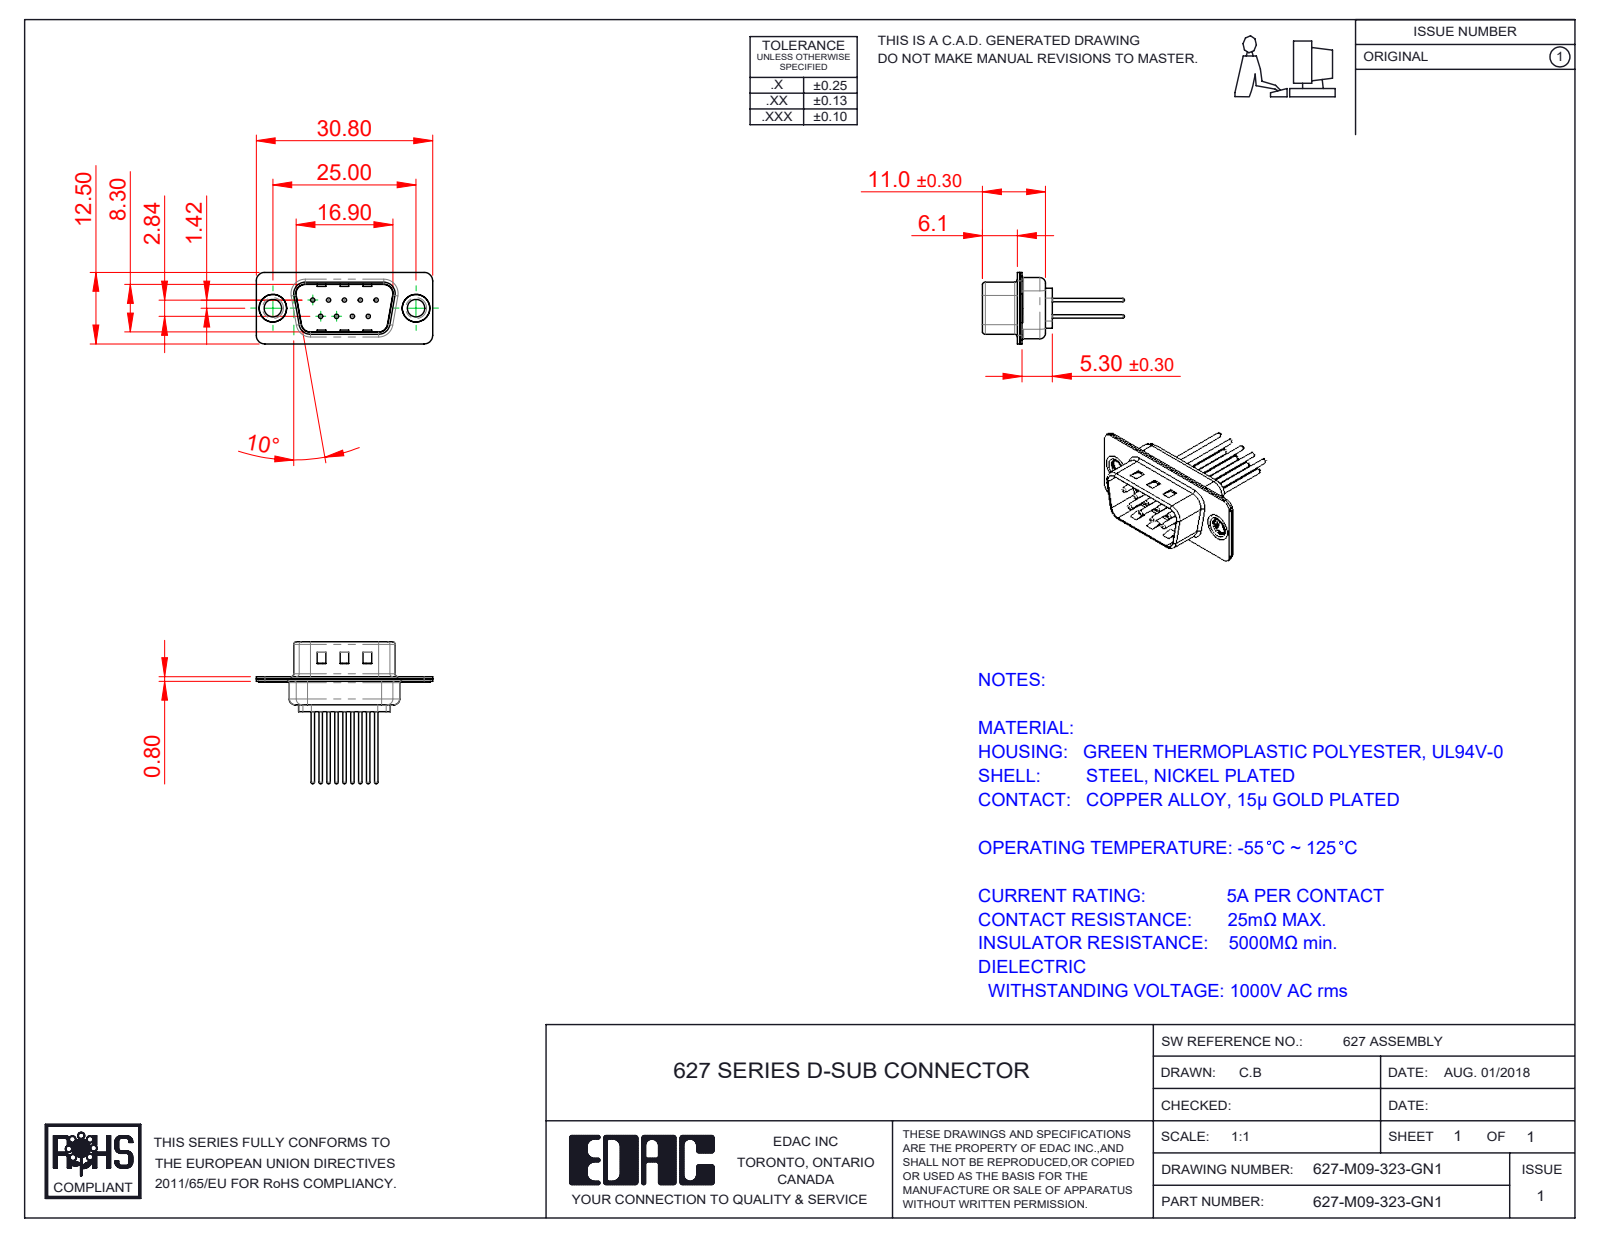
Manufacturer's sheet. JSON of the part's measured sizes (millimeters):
{"part_name": "627-M09-323-GN1; 627M Shell Front_09 Contacts; 627M Shell Rear_09 Contacts; 627M Contact Row 2_23 (+3 more)", "step_written_by": "SolidWorks 2020 (CONFIG_CONTROL_DESIGN)", "units": "millimeters", "bodies": {"solids": 14, "faces": 611, "planar": 170, "cylindrical": 239, "other": 202}, "overall_size": [30.8, 24.77, 12.5], "volume_mm3": 1250, "surface_area_mm2": 3545, "round_holes": [[0.75, 9], [1.6, 9], [2, 9], [3.05, 2], [4, 2], [4.8, 2]], "round_bosses_or_shafts": [[1.5, 9], [0.6, 9], [5, 2], [4.9, 2], [3.55, 2]], "partial_cylinders_radius": [[1.5, 16], [2, 12], [0.5, 8], [1.6, 8], [0.25, 4], [0.6, 4], [0.65, 4], [0.9, 4]], "face_to_face_distances": [0.4, 0.8, 9.5, 9.1, 8.7, 0.65, 9.9, 1.2, 6.1, 5.3], "hole_center_spacings": [3.16, 2.77, 5.54, 5.03, 5.04, 8.31, 7.1, 7.48]}
